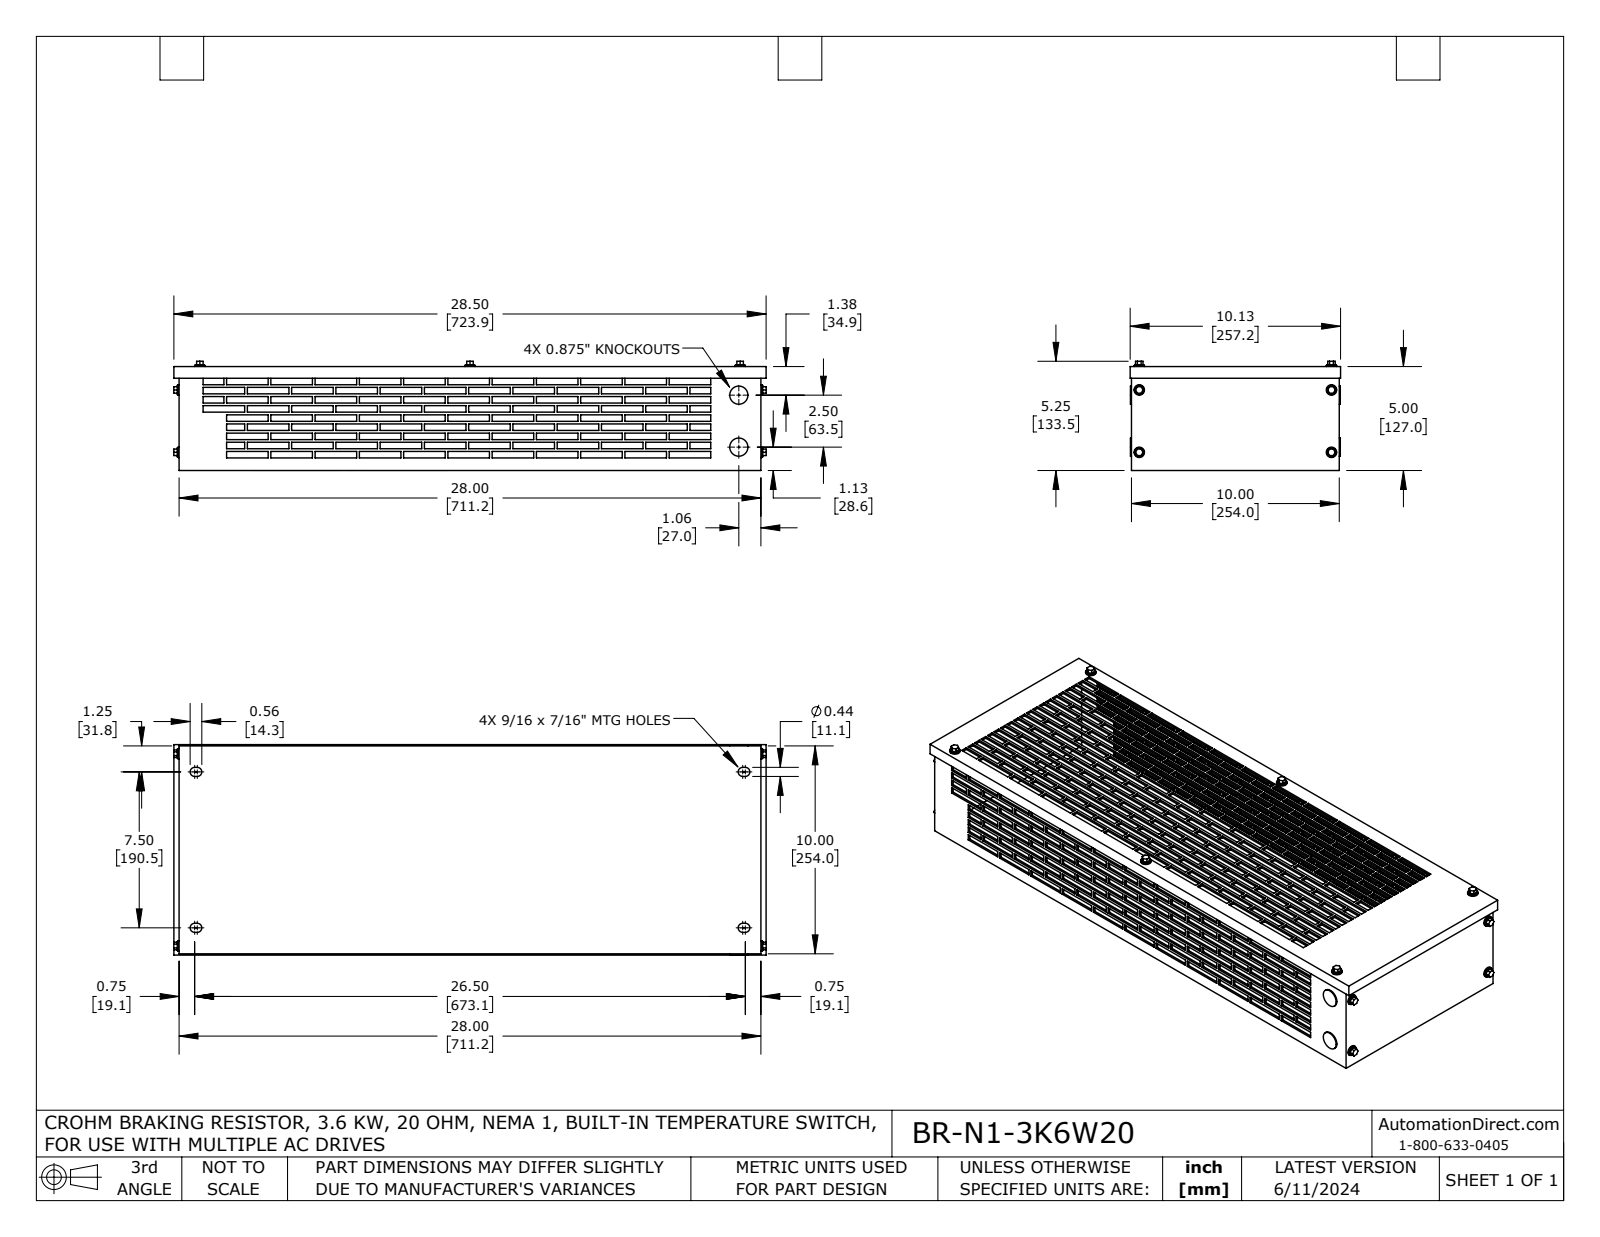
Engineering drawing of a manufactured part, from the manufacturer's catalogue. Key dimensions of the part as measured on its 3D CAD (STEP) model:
Part name (STEP PRODUCT): BR-N1-3K6W20
STEP written by: SolidWorks 2021 (AUTOMOTIVE_DESIGN)
Units: inches
Bodies: 33 solids, 2040 faces (1932 planar, 108 cylindrical, 0 other)
Overall size (bounding box): 28.509 × 10.125 × 5.254
Volume: 68.03 in³ · Surface area: 1 567 in²
Round holes (diameter × count): ⌀0.25 ×10, ⌀0.75 ×2
Round bosses / shafts (diameter × count): ⌀0.5 ×10, ⌀0.437 ×10, ⌀0.875 ×2
Partial cylindrical surfaces — rounded edges, fillets, slot ends (radius × count): R0.219 ×8
Main face-to-face distances: 0.1, 4.9, 5, 4.8, 9.9, 27.9, 10, 9.8, 0.88, 0.063
Hole centre spacings: 9.25, 13, 15.955, 3, 9.724, 26, 27.596, 2.5
